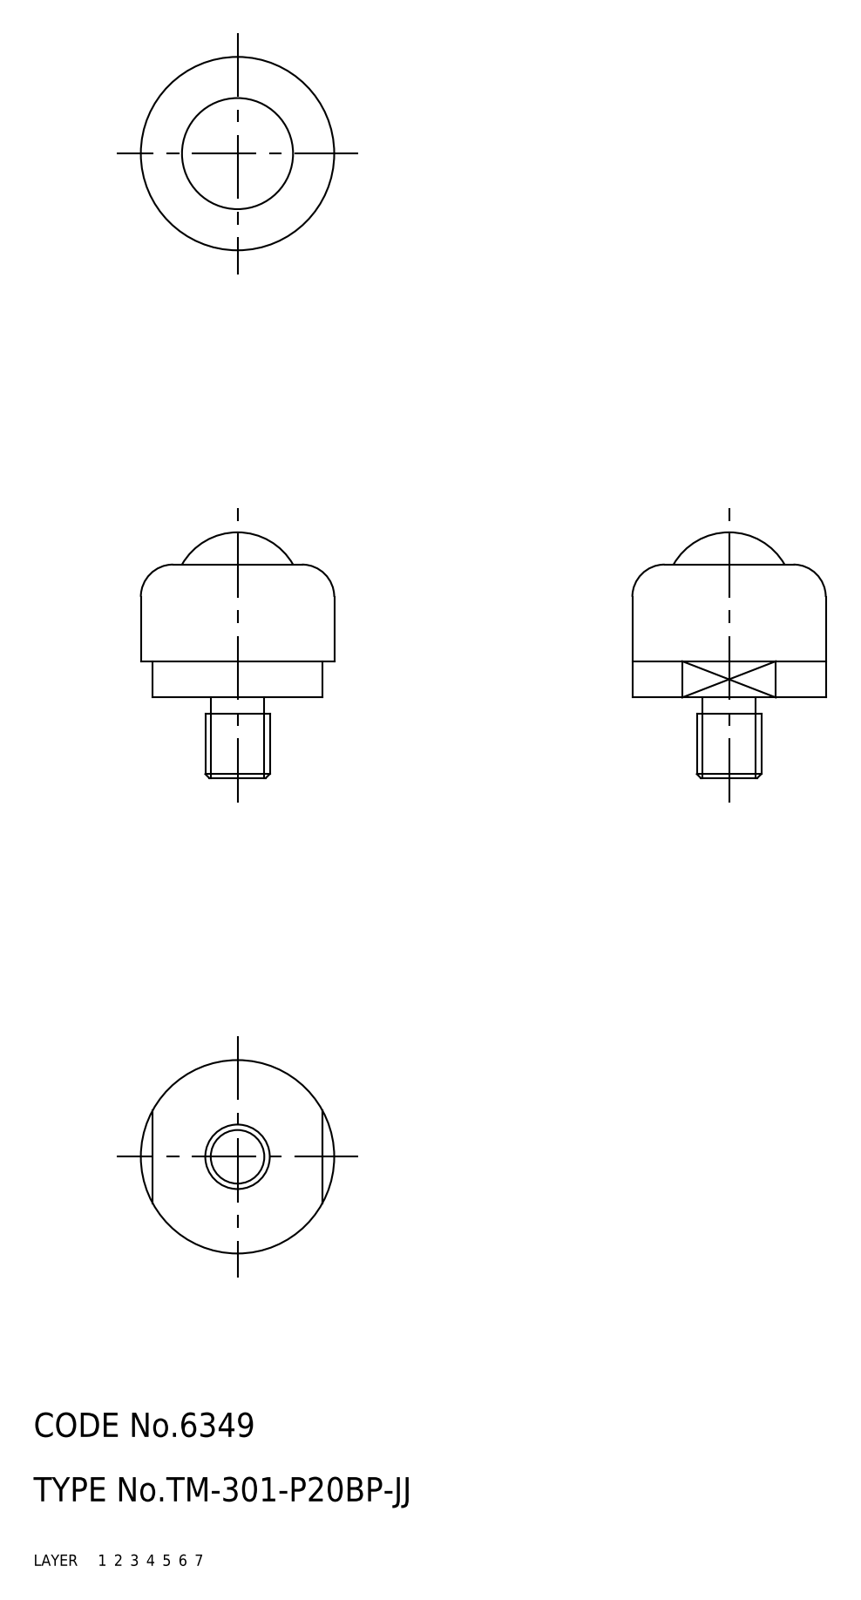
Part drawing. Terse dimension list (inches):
name: 67111097; 67111110; 67111123
written by: CADfix (AUTOMOTIVE_DESIGN)
unit: in
bodies: 3 solids, 29 faces (0 planar, 0 cylindrical, 29 other)
size: 1.201 × 0.945 × 0.945
volume: 0.317 in³; area: 6.702 in²
